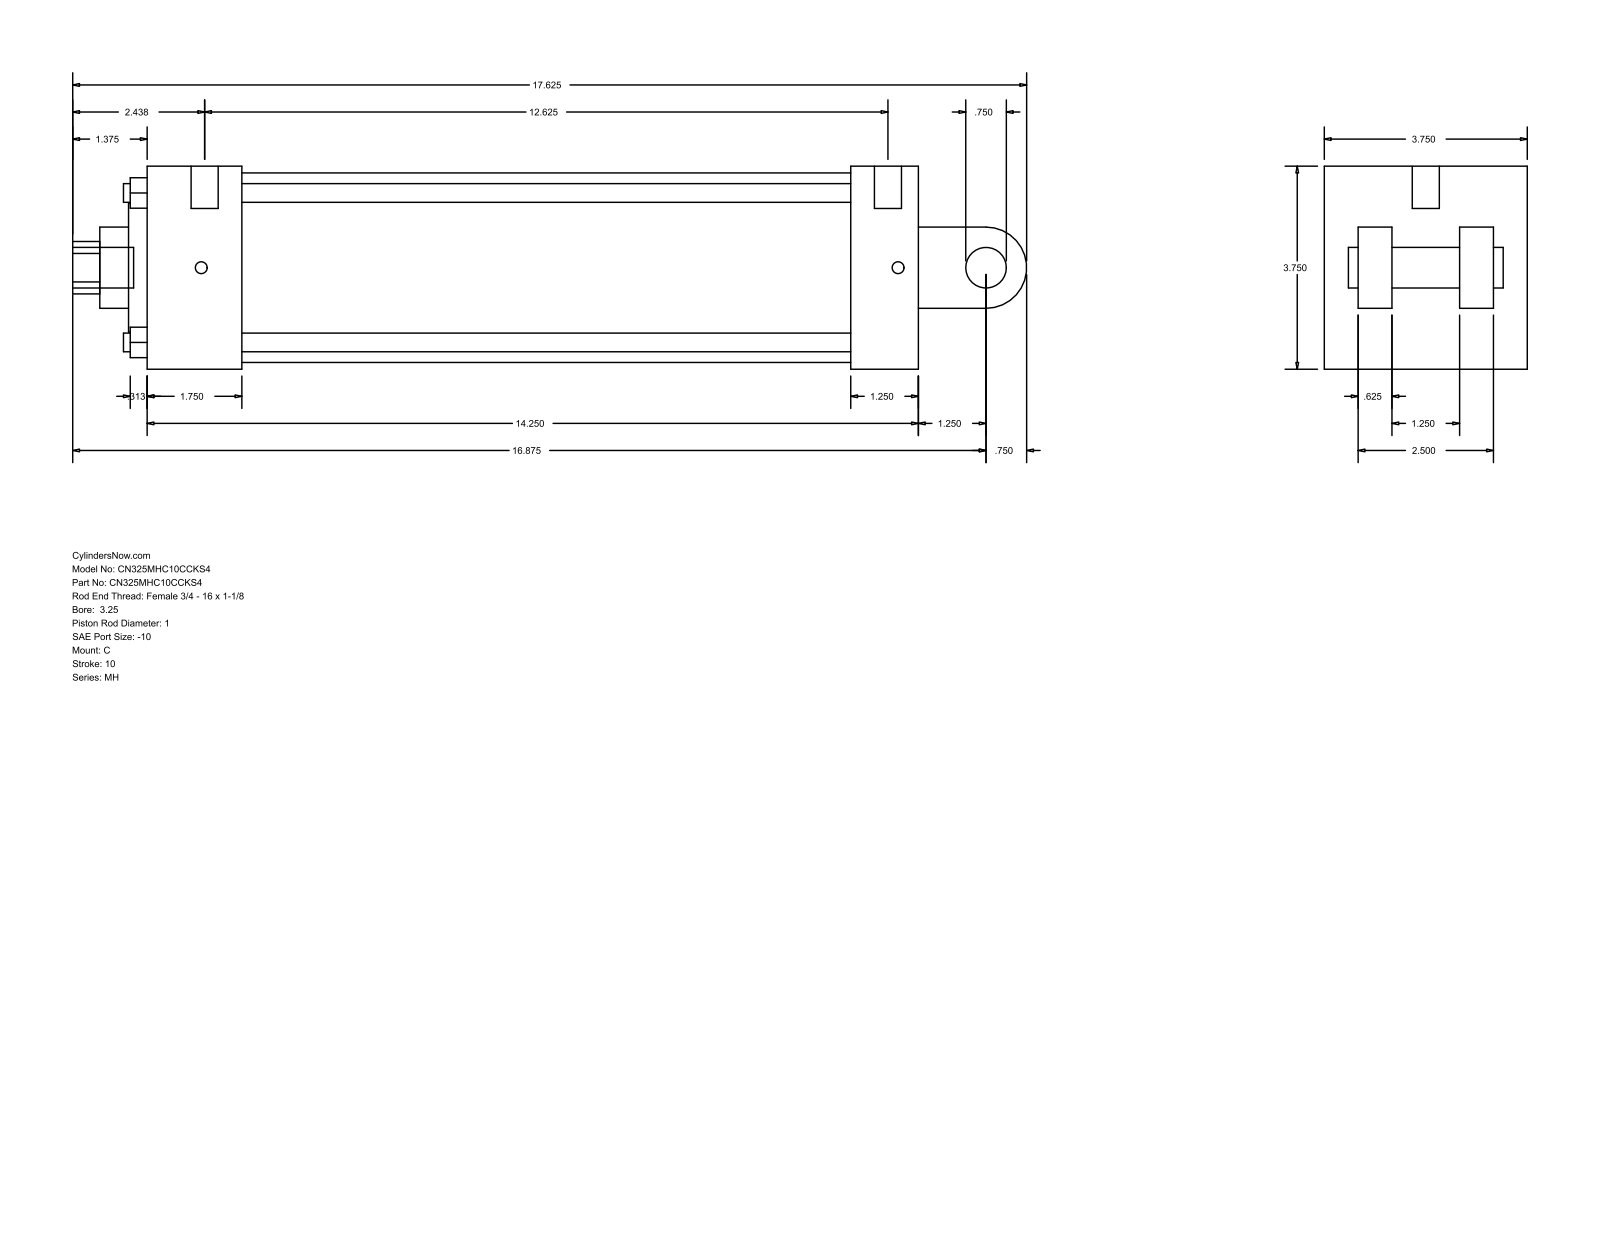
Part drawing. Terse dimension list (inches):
name: MH_C__0325_1
written by: GSSL Pune (CONFIG_CONTROL_DESIGN)
unit: in
bodies: 0 solids, 101 faces (71 planar, 30 cylindrical, 0 other)
size: 17.625 × 3.75 × 3.75
holes: 4× ⌀0.345, 2× ⌀0.219, 1× ⌀0.5, 1× ⌀1, 1× ⌀1.5, 1× ⌀2.375, 1× ⌀3.5
bosses: 2× ⌀0.75, 2× ⌀0.219, 1× ⌀0.5
rounds: 1× R0.484, 1× R0.75
face distances: 3.75, 0.625, 14.25, 2.5, 1.25, 3.125, 1.25, 1.875, 1.75, 13
hole spacings: 1.952, 2.76, 3.903, 0.187
